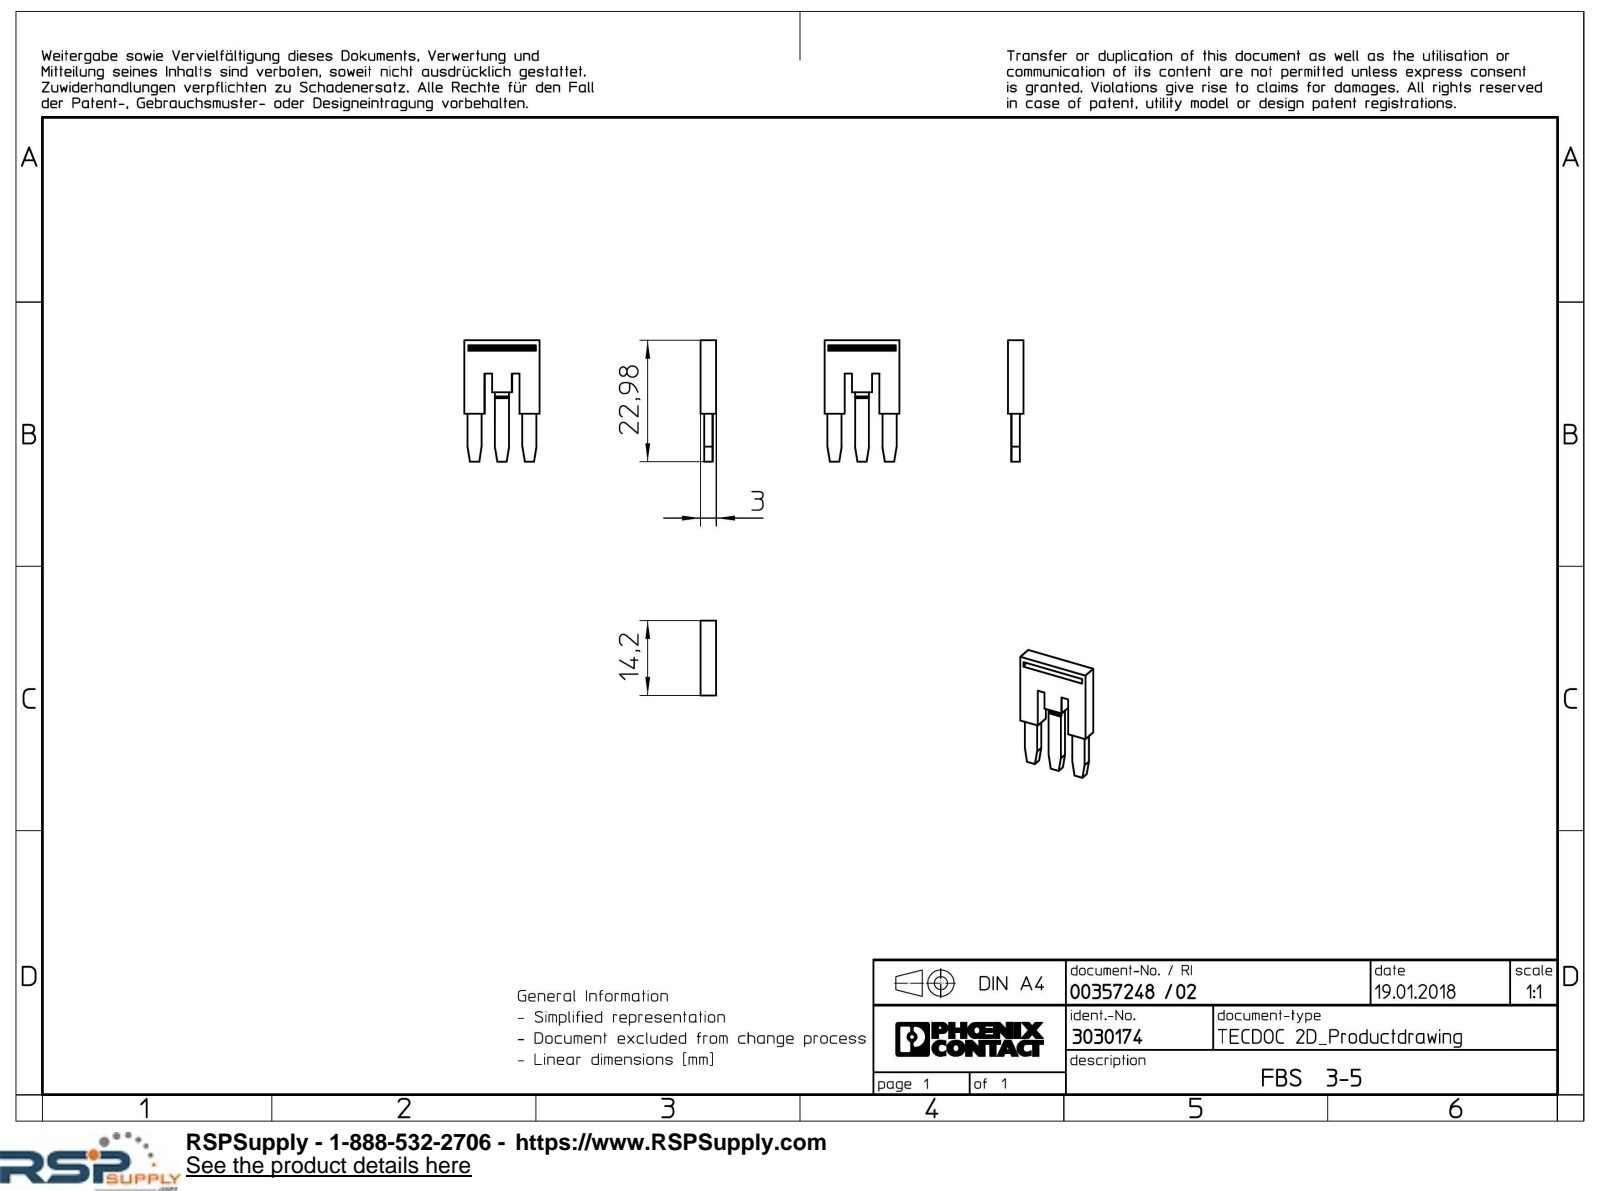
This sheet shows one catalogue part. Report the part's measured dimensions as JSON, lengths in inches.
{"part_name": "FBS_3_5-select", "step_written_by": "Creo Elements/Direct Modeling 20.1A 29-Sep-2018 (C) Parametric Technology GmbH (AUTOMOTIVE_DESIGN)", "units": "inches", "bodies": {"solids": 1, "faces": 51, "planar": 51, "cylindrical": 0, "other": 0}, "overall_size": [0.905, 0.559, 0.118], "volume_in3": 0.036, "surface_area_in2": 1.32, "face_to_face_distances": [0.028, 0.091, 0.118, 0.205, 0.063, 0.409, 0.022, 0.128, 0.15, 0.332]}
